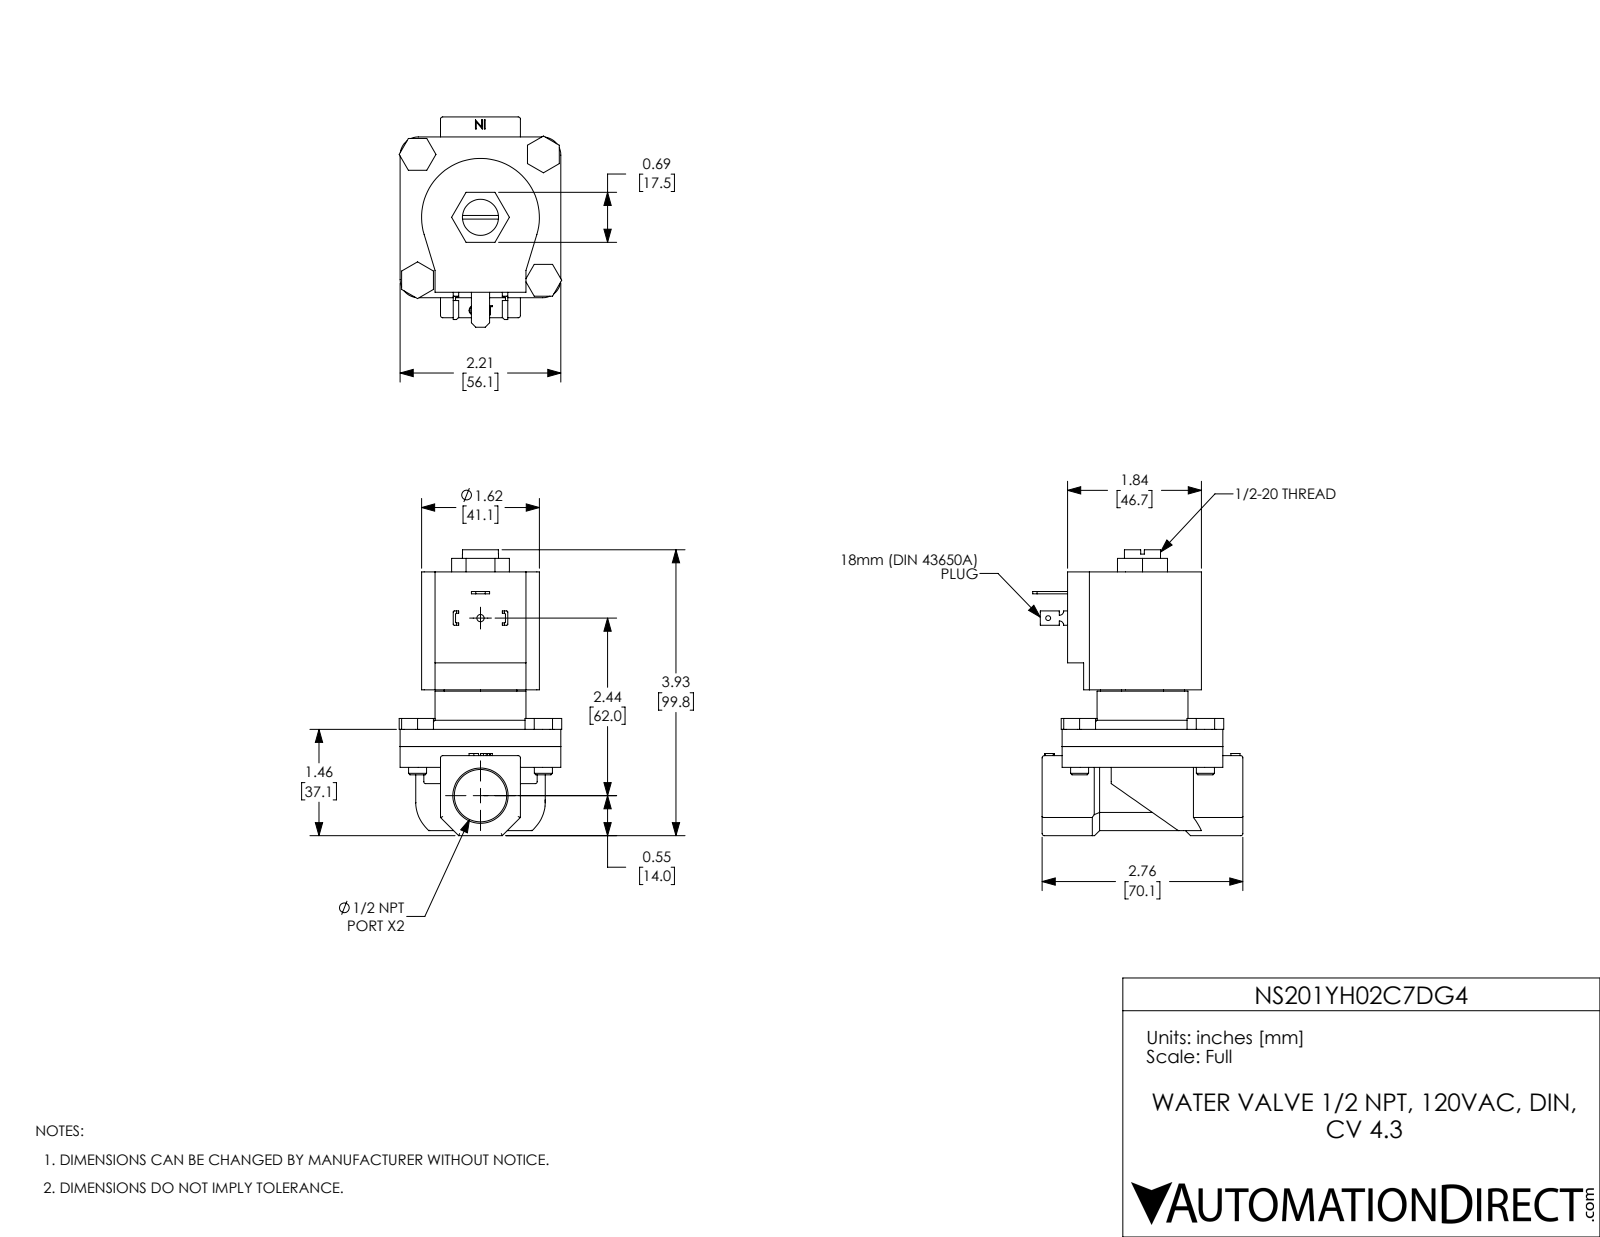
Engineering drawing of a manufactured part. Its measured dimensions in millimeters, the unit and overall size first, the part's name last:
Units: millimetres
Overall size (bounding box): 99.8 × 73.4 × 56.8
Round holes (diameter × count): ⌀6.4 ×4, ⌀1.7 ×1, ⌀2.5 ×1, ⌀12.6 ×1, ⌀13 ×1, ⌀18.3 ×1, ⌀29.3 ×1
Round bosses / shafts (diameter × count): ⌀6.3 ×4, ⌀31.8 ×1
Partial cylindrical surfaces — rounded edges, fillets, slot ends (radius × count): R0.8 ×15, R0.4 ×8, R6.4 ×4, R1.5 ×2, R20.6 ×1, R22.6 ×1
Main face-to-face distances: 6, 6, 61, 61, 54.9, 14.1, 42, 7.3, 7.3, 13.3
Hole centre spacings: 31.1, 43.9, 62.1, 62
Volume: 160 900 mm³ · Surface area: 40 930 mm²
Bodies: 11 solids, 330 faces (196 planar, 99 cylindrical, 35 other)
Part name (STEP PRODUCT): NS201YH02C7DG4
STEP written by: SolidWorks 2024 (CONFIG_CONTROL_DESIGN)
